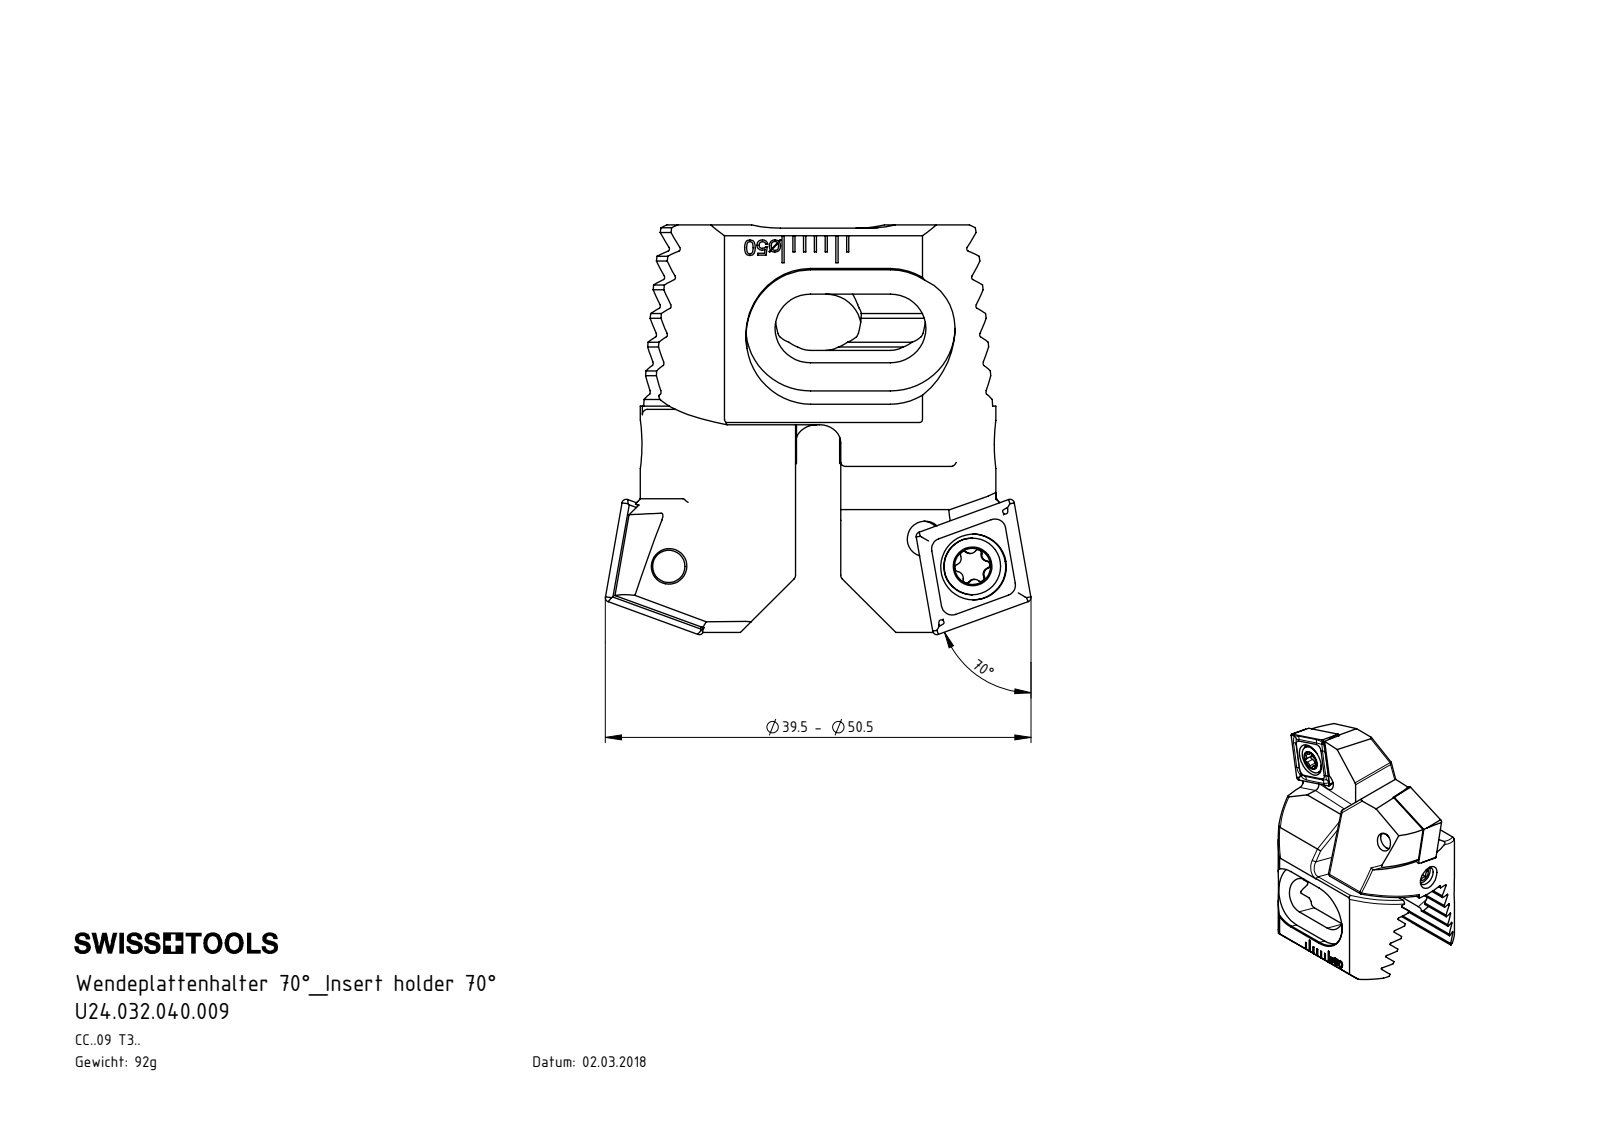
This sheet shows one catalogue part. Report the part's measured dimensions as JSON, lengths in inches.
{"part_name": "Z32-ER3.001.013_A; Z32-xxx.001.021_B_70ø; Z32.WCB.B70.021; WCB-ER2.001.009_A (+1 more)", "step_written_by": "SolidWorks 2017 (AUTOMOTIVE_DESIGN)", "units": "inches", "bodies": {"solids": 8, "faces": 574, "planar": 298, "cylindrical": 104, "other": 172}, "overall_size": [1.555, 1.496, 1.031], "volume_in3": 0.717, "surface_area_in2": 12.7, "round_holes": [[0.13, 4], [0.063, 2], [0.173, 2], [0.24, 2], [0.079, 1], [0.138, 1]], "round_bosses_or_shafts": [[0.157, 3], [0.207, 2]], "partial_cylinders_radius": [[0.02, 16], [0.008, 12], [0.013, 12], [0.023, 12], [0.039, 4], [0.079, 4], [0.13, 4], [0.236, 4]], "face_to_face_distances": [0.094, 0.187, 0.375, 0.281, 0.193, 0.469, 0.281, 0.05, 0.188, 0.094], "hole_center_spacings": [0.2, 0.204, 0.354, 0.958, 0.961, 1.13, 0.684, 0.779]}
